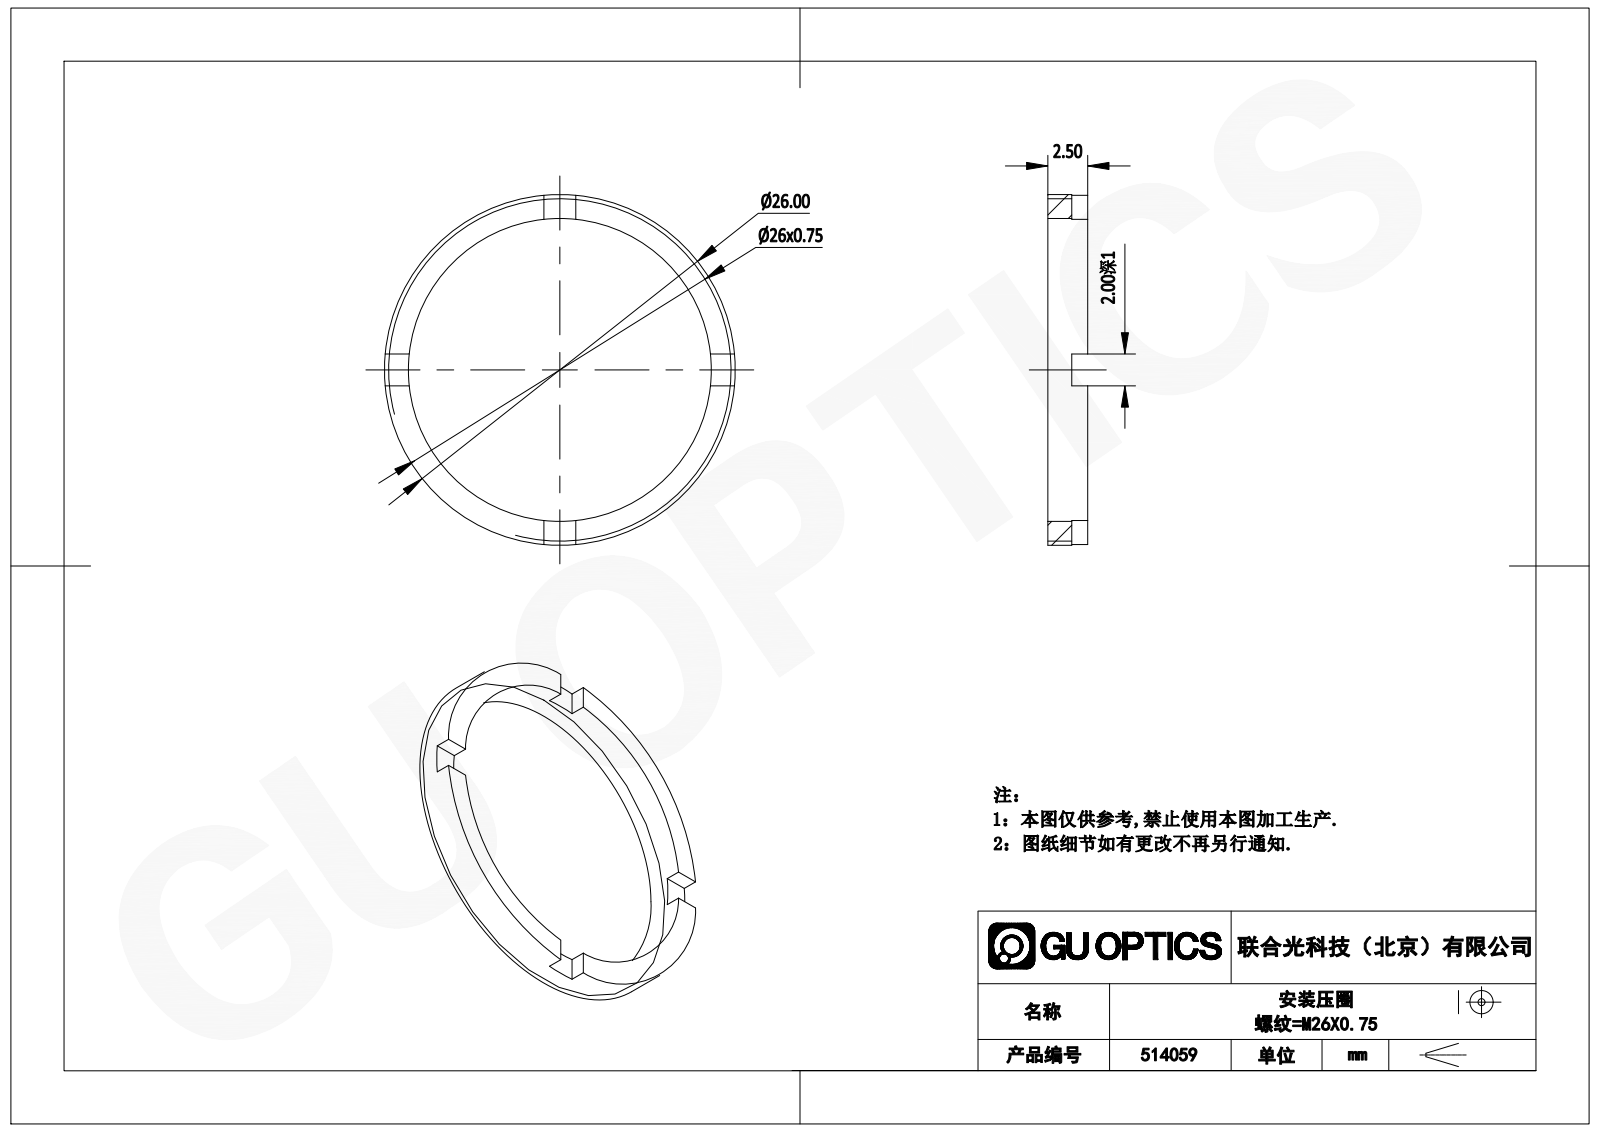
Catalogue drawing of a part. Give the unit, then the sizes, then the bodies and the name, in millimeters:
Units: millimetres
Overall size (bounding box): 26 × 26 × 2.5
Round holes (diameter × count): ⌀23 ×1
Round bosses / shafts (diameter × count): ⌀26 ×1
Main face-to-face distances: 2.5, 1.5, 1, 2
Volume: 277 mm³ · Surface area: 612 mm²
Bodies: 1 solid, 21 faces (17 planar, 4 cylindrical, 0 other)
Part name (STEP PRODUCT): 514059
STEP written by: SolidWorks 2020 (CONFIG_CONTROL_DESIGN)
